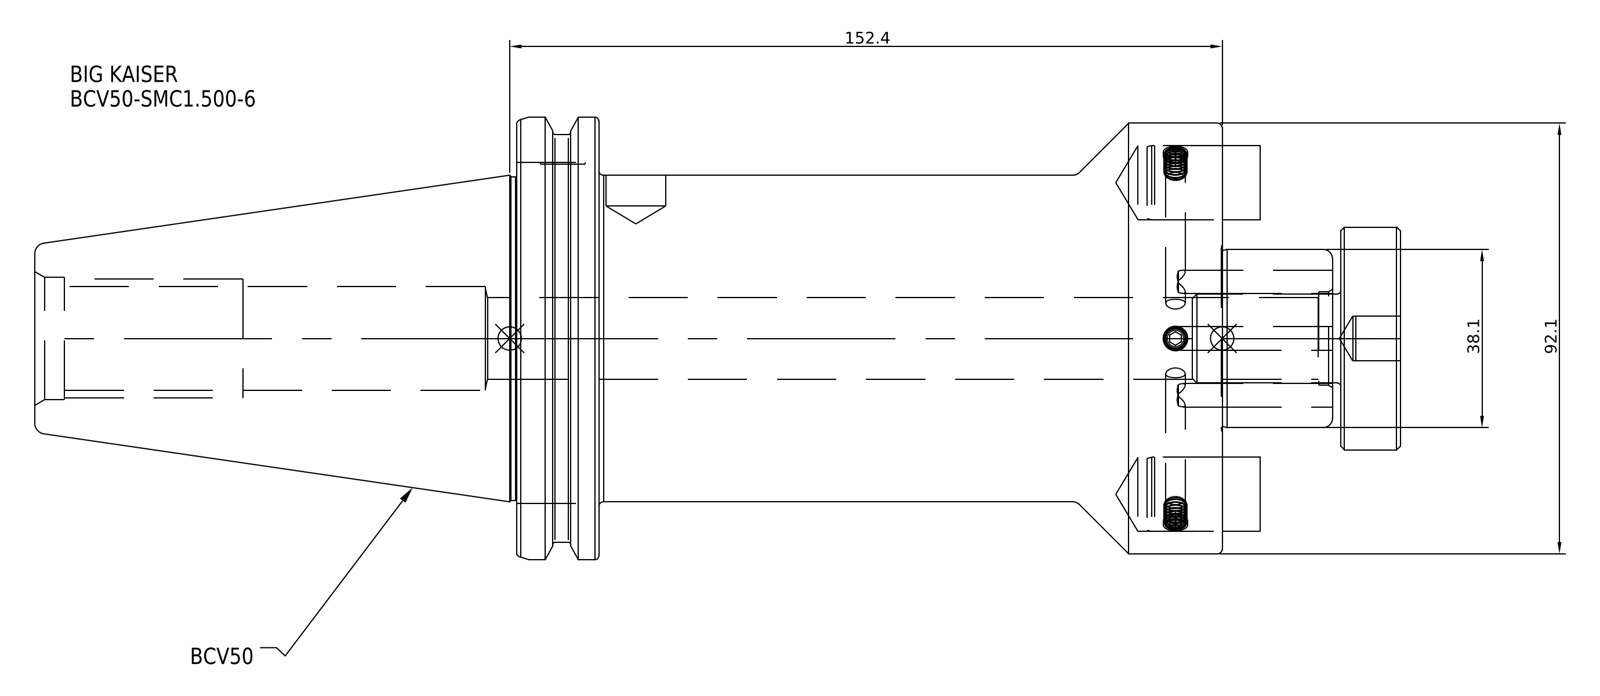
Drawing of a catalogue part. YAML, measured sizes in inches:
part_name: "BCV50-SMC1_500-6"
step_written_by: "SolidWorks 2021 (CONFIG_CONTROL_DESIGN)"
units: inches
bodies: {solids: 1, faces: 39, planar: 17, cylindrical: 14, other: 8}
overall_size: [10.318, 3.875, 3.875]
volume: 57.36
surface_area: 124
round_holes:
  - {diameter: 0.687, count: 1}
round_bosses_or_shafts:
  - {diameter: 3.875, count: 1}
  - {diameter: 3.626, count: 1}
  - {diameter: 3.594, count: 1}
  - {diameter: 2.75, count: 1}
face_to_face_distances: [5.941, 5.25, 0.691, 10, 4.75, 4.059, 0.625, 0.318, 5.568, 6.259]
